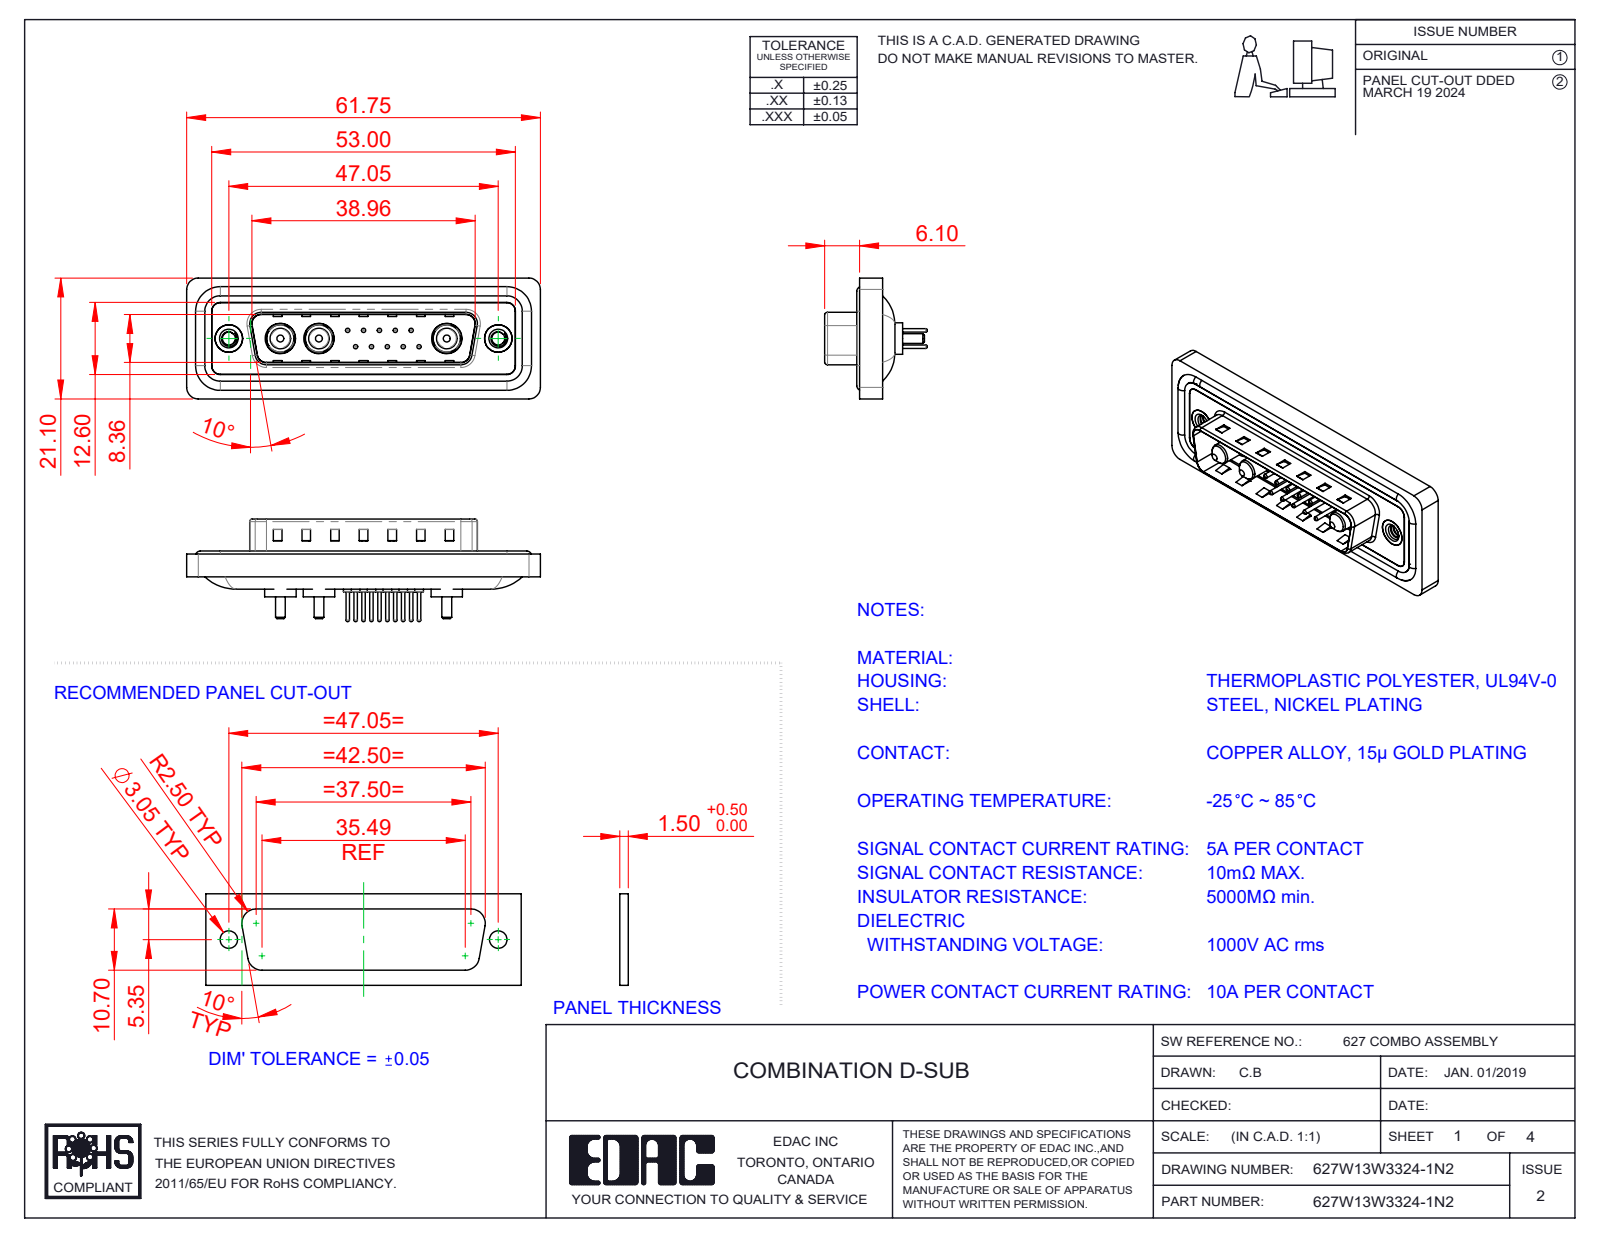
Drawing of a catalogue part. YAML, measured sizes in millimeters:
part_name: "627Combo Waterproof Housing_25 Contacts; 627Combo Contact Row 2_24; 627W13W3324-1N2; 627Combo Contact Row 1_24 (+5 more)"
step_written_by: "SolidWorks 2023 (CONFIG_CONTROL_DESIGN)"
units: millimeters
bodies: {solids: 23, faces: 970, planar: 309, cylindrical: 385, other: 276}
overall_size: [61.75, 21.1, 17.9]
volume: 7291
surface_area: 11837
round_holes:
  - {diameter: 0.75, count: 10}
  - {diameter: 1.6, count: 10}
  - {diameter: 2, count: 10}
  - {diameter: 4.85, count: 3}
  - {diameter: 5.3, count: 3}
  - {diameter: 2.26, count: 2}
  - {diameter: 4, count: 2}
  - {diameter: 4.8, count: 2}
  - {diameter: 5, count: 2}
round_bosses_or_shafts:
  - {diameter: 1.5, count: 10}
  - {diameter: 0.6, count: 10}
  - {diameter: 1.6, count: 4}
  - {diameter: 5.5, count: 3}
  - {diameter: 5.2, count: 3}
  - {diameter: 4.75, count: 3}
  - {diameter: 3.75, count: 3}
  - {diameter: 3.6, count: 3}
partial_cylinders:
  - {radius: 1.5, count: 22}
  - {radius: 2, count: 18}
  - {radius: 0.5, count: 8}
  - {radius: 1.6, count: 8}
  - {radius: 0.25, count: 4}
  - {radius: 0.6, count: 4}
  - {radius: 0.65, count: 4}
  - {radius: 0.9, count: 4}
face_to_face_distances: [0.4, 1.5, 1.1, 1.6, 0.5, 3.1, 2.9, 0.82, 9.58, 4.1]
hole_center_spacings: [3.16, 2.77, 5.04, 5.54, 7.49, 5.03, 8.31, 10.11]
